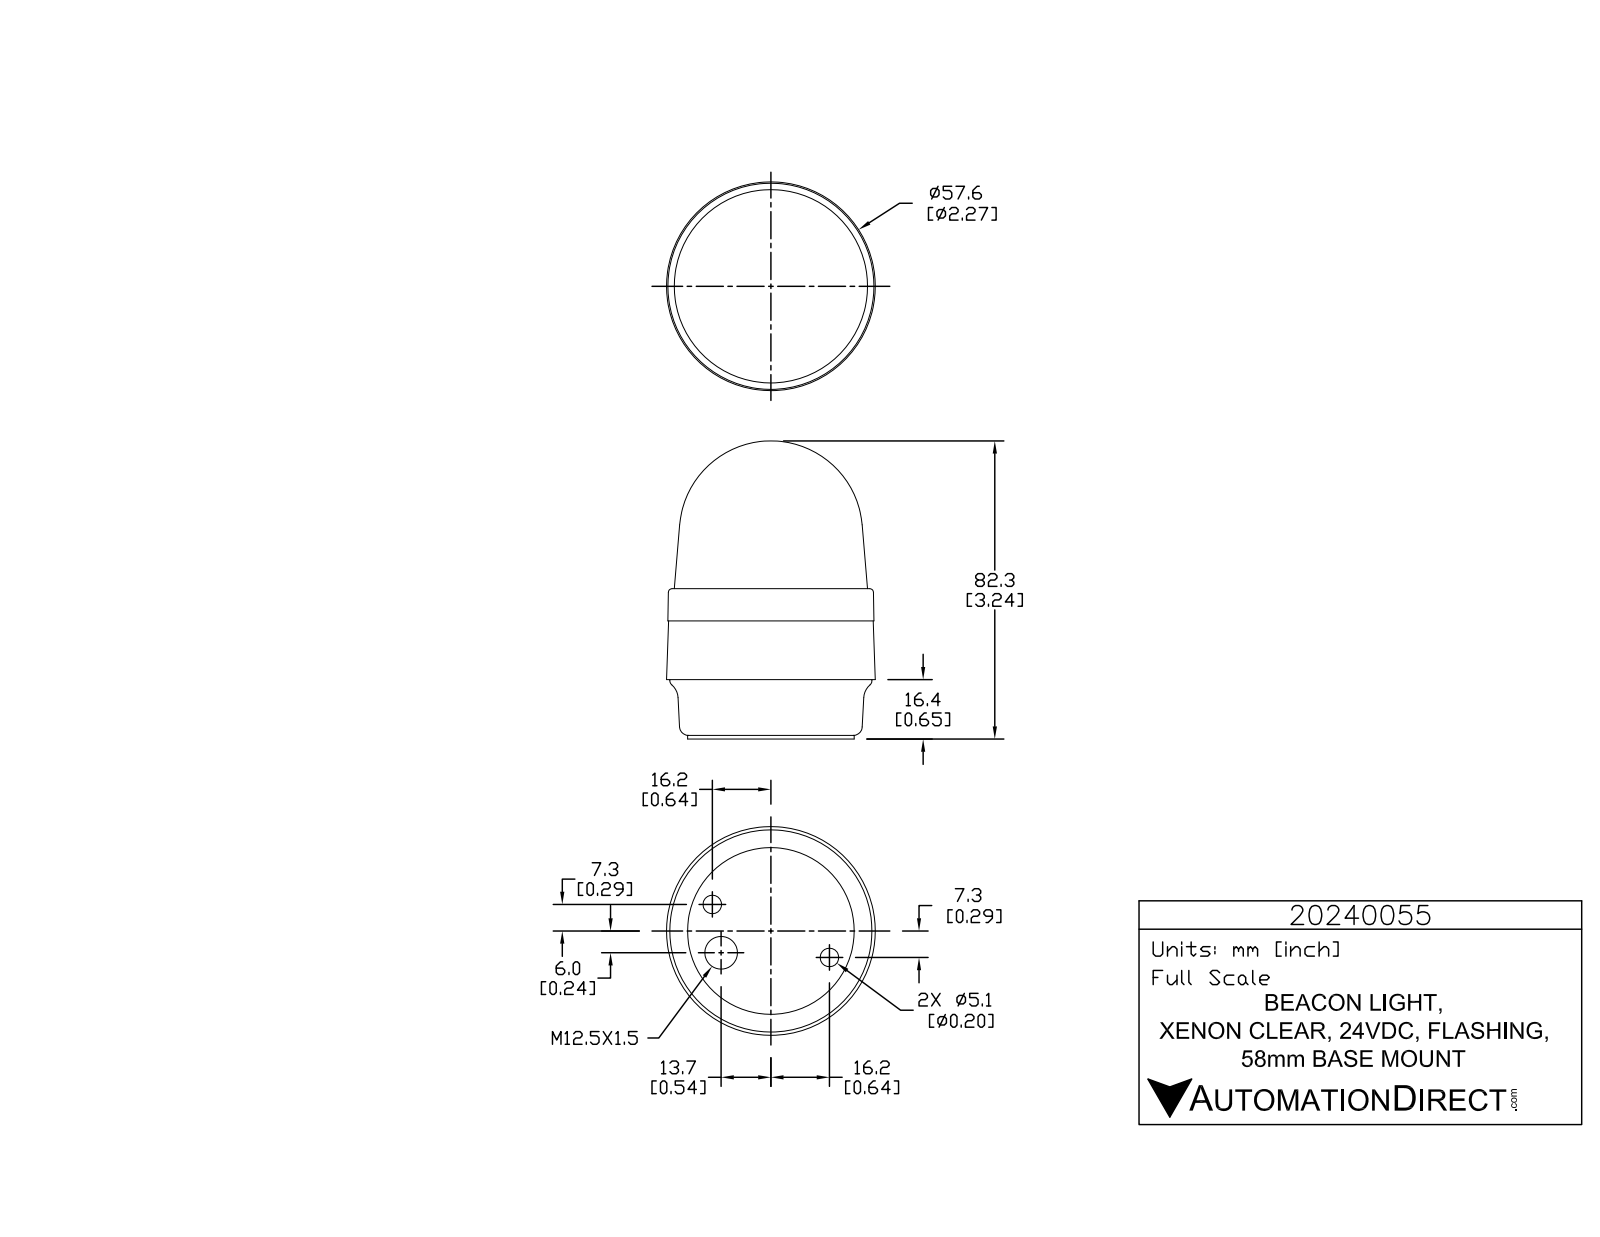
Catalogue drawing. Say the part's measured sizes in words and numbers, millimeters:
The part is named "20240055". Its 3-D file was written by "SolidWorks 2015 (AUTOMOTIVE_DESIGN)". It is 1 solid with 763 faces: 527 planar, 145 cylindrical and 91 other. Overall it measures 82.3 by 57.63 by 57.63 millimeters. Its volume is 164 395 cubic millimeters and its surface area 16 261 square millimeters. Round holes: 3 of diameter 0.99, 2 of diameter 5.11, 1 of diameter 9. Round bosses or shafts: 3 of diameter 5.74, 3 of diameter 1.43, 1 of diameter 55.8, 1 of diameter 46. Partial cylindrical surfaces (rounded edges, fillets, slot ends): 6 of radius 0.2, 6 of radius 0.21, 6 of radius 0.21, 6 of radius 3.32, 3 of radius 0.1, 3 of radius 0.12, 3 of radius 0.19, 3 of radius 0.2. The main face-to-face distances are 16.4, 1, 15.4, 41.5, 40.5, 25.1, 32.6, 31.6, 16.2, 8.9. The hole center spacings are 13.56, 29.94, 35.5.
